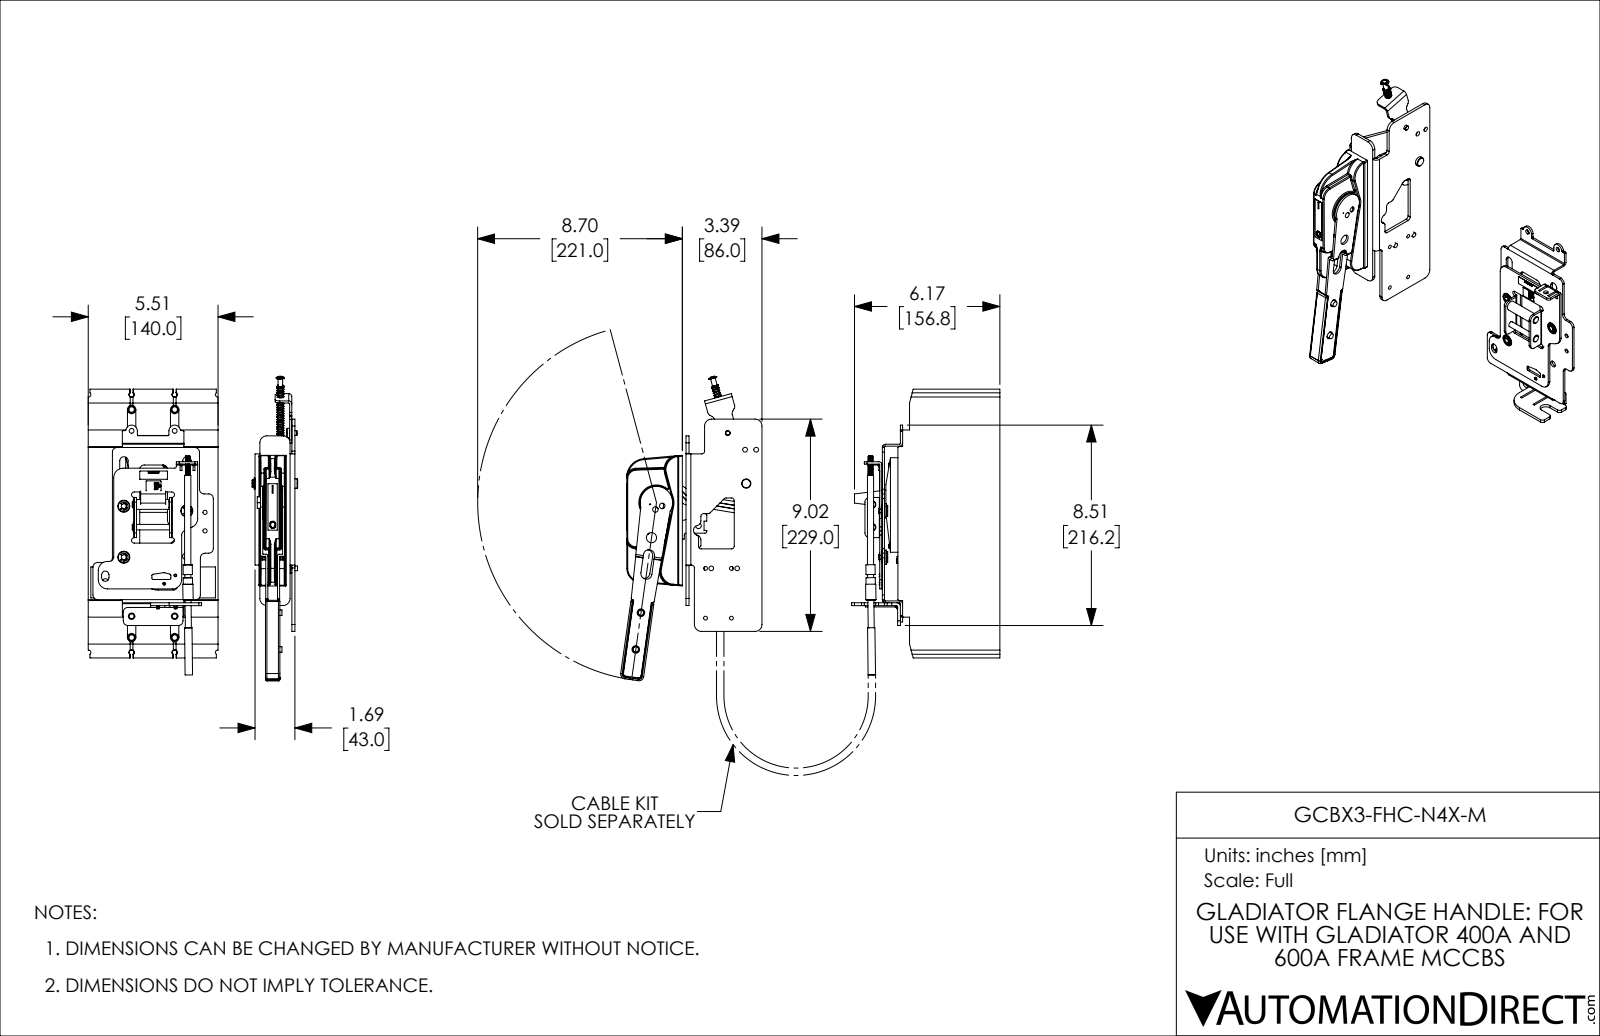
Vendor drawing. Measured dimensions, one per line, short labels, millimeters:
name: GCBX3-FHC-N4X-M_2; GCBX3-FHC-N4X-M_1; GCB400H-3FF400LL; GCBX3-CBL-36_2 (+1 more)
written by: SolidWorks 2021 (CONFIG_CONTROL_DESIGN)
unit: mm
bodies: 94 solids, 4312 faces (2593 planar, 1247 cylindrical, 472 other)
size: 409.3 × 328.6 × 226
volume: 4 352 000 mm³; area: 585 700 mm²
holes: 11× ⌀6, 9× ⌀6, 8× ⌀5, 8× ⌀5.2, 6× ⌀10.5, 6× ⌀15.1, 6× ⌀17.5, 5× ⌀4, 5× ⌀5.1, 5× ⌀6.2, 5× ⌀7, 4× ⌀4.2
bosses: 13× ⌀10, 8× ⌀6, 6× ⌀14.6, 6× ⌀5, 5× ⌀8, 4× ⌀13, 3× ⌀15.5, 3× ⌀8.8
rounds: 96× R1, 44× R3, 42× R5, 30× R0.2, 30× R0.5, 29× R2.5, 27× R1.5, 23× R2
face distances: 140, 2.3, 46.5, 3.2, 12.5, 83, 37, 2.8, 5, 3
hole spacings: 46.5, 24.6, 27.7, 33.4, 216.3, 239.1, 255.1, 16
